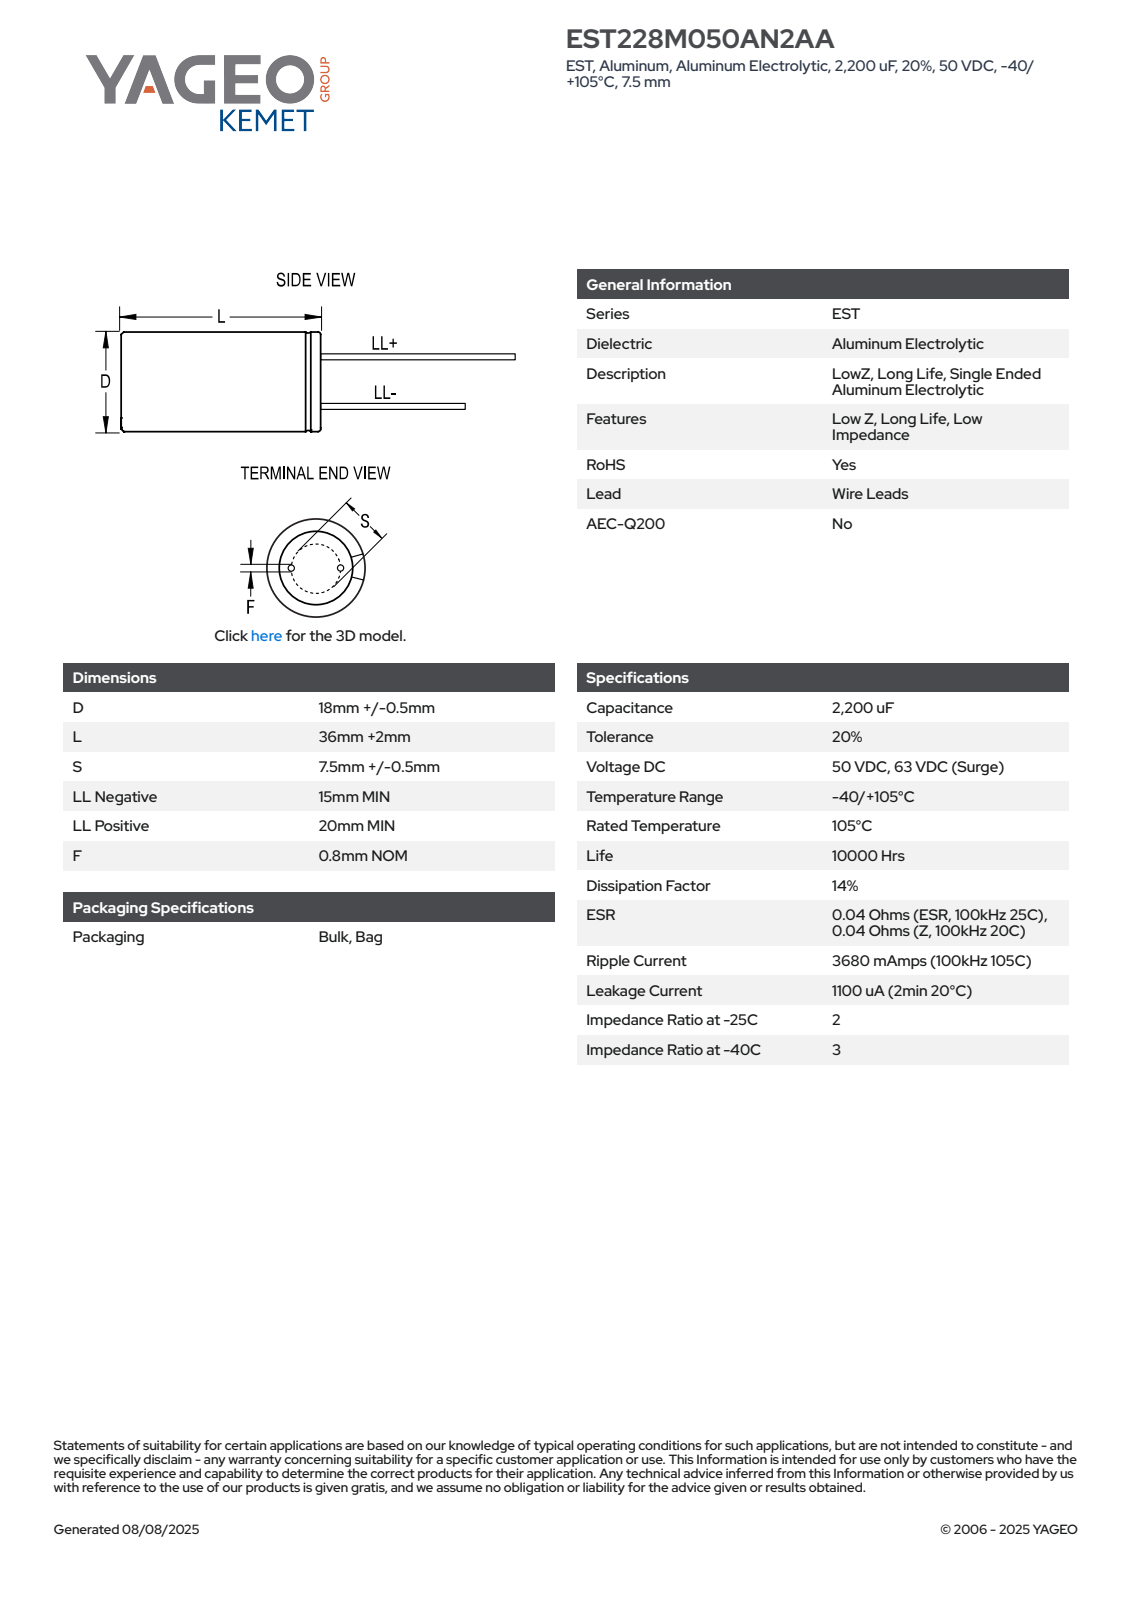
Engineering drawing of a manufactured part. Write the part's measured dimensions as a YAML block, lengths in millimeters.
part_name: "CAR_KLP_18X36_D18.5L38S7.5F0.8"
step_written_by: "SolidWorks 2014 (AUTOMOTIVE_DESIGN)"
units: millimeters
bodies: {solids: 4, faces: 75, planar: 61, cylindrical: 8, other: 6}
overall_size: [58.01, 18.5, 18.5]
volume: 10166
surface_area: 2914
round_bosses_or_shafts:
  - {diameter: 0.8, count: 2}
  - {diameter: 18.5, count: 1}
face_to_face_distances: [38, 38.01, 53.01, 58.01, 53, 58, 15, 20, 5, 2.48]
